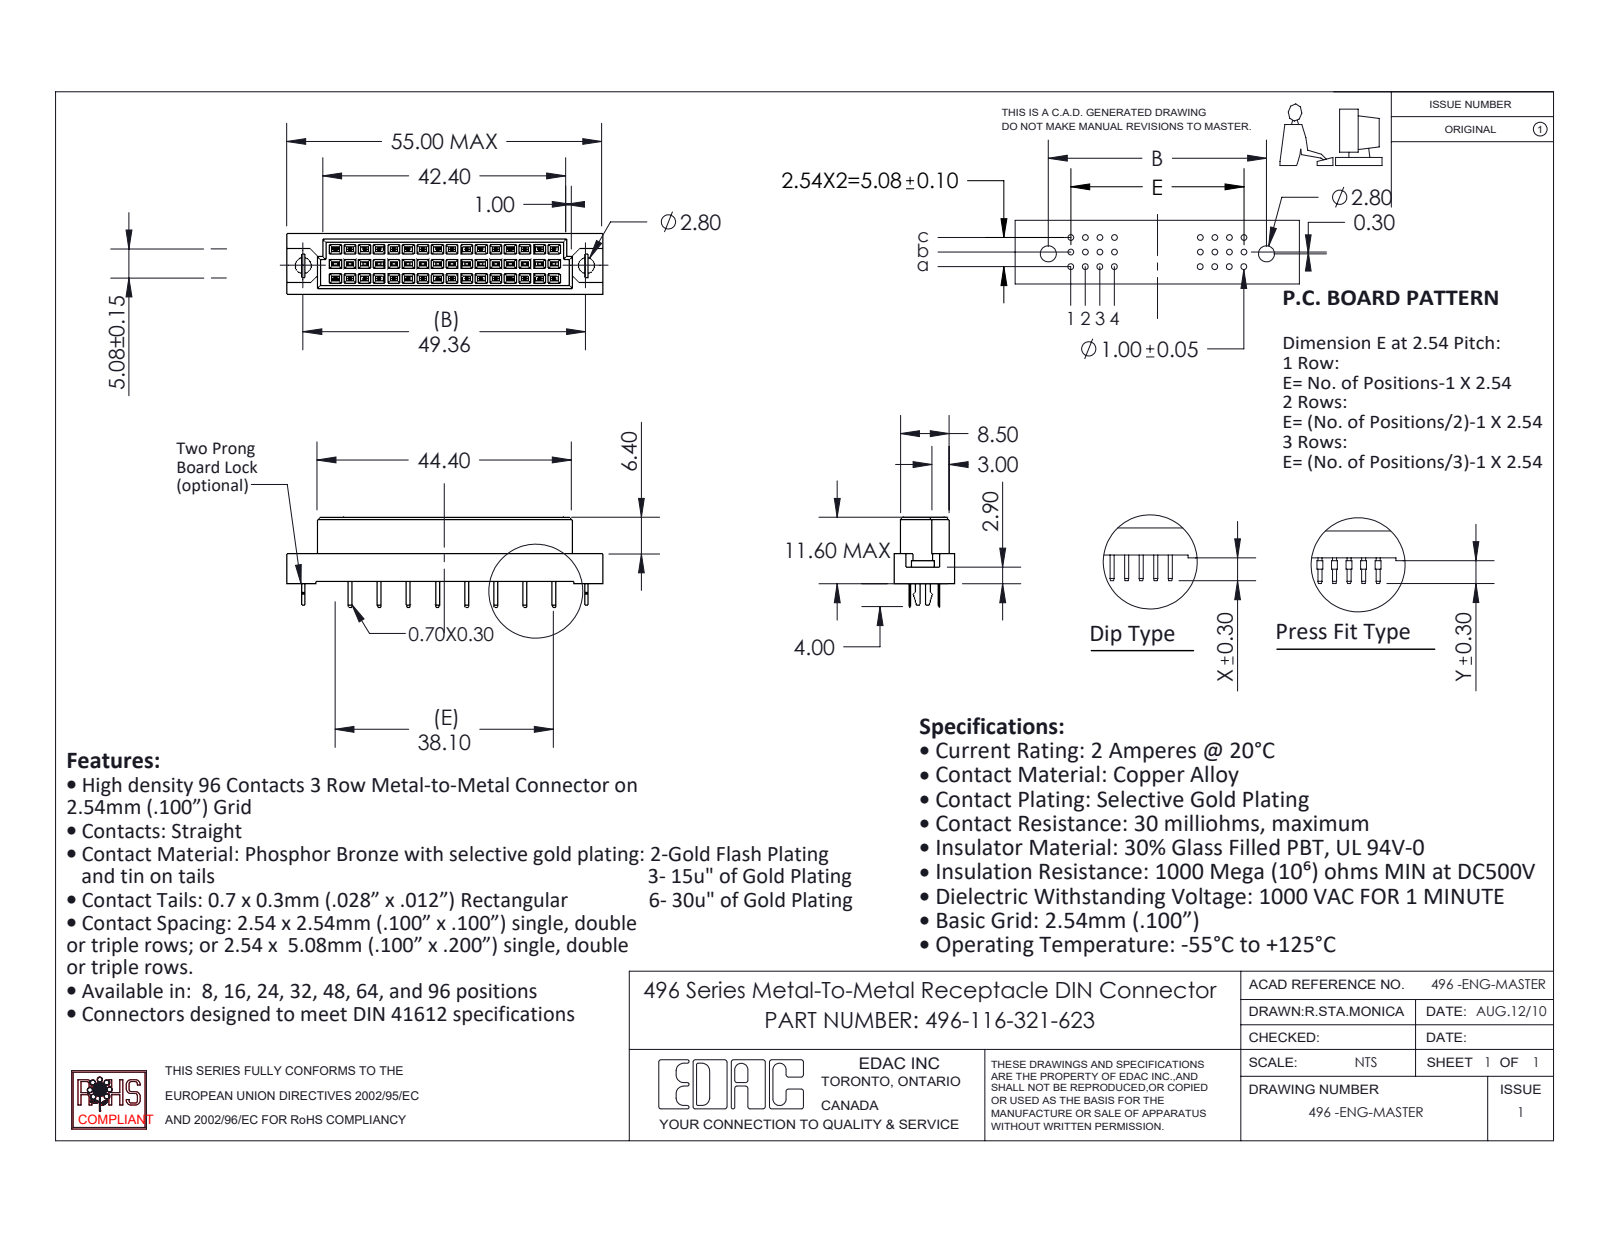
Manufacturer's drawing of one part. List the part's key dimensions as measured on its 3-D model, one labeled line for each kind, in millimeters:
Part name (STEP PRODUCT): 496-290_21; 496 Bore-lock; 496 Part_48; 496-116-321-623
STEP written by: SolidWorks 2020 (CONFIG_CONTROL_DESIGN)
Units: millimetres
Bodies: 19 solids, 862 faces (856 planar, 6 cylindrical, 0 other)
Overall size (bounding box): 55 × 15.6 × 10.6
Volume: 4 640 mm³ · Surface area: 4 601 mm²
Round holes (diameter × count): ⌀2.8 ×2
Partial cylindrical surfaces — rounded edges, fillets, slot ends (radius × count): R0.53 ×1
Main face-to-face distances: 2.54, 5.08, 1.05, 9.55, 0.81, 10.6, 0.56, 3.35, 1.73, 8.5
Hole centre spacings: 49.36
